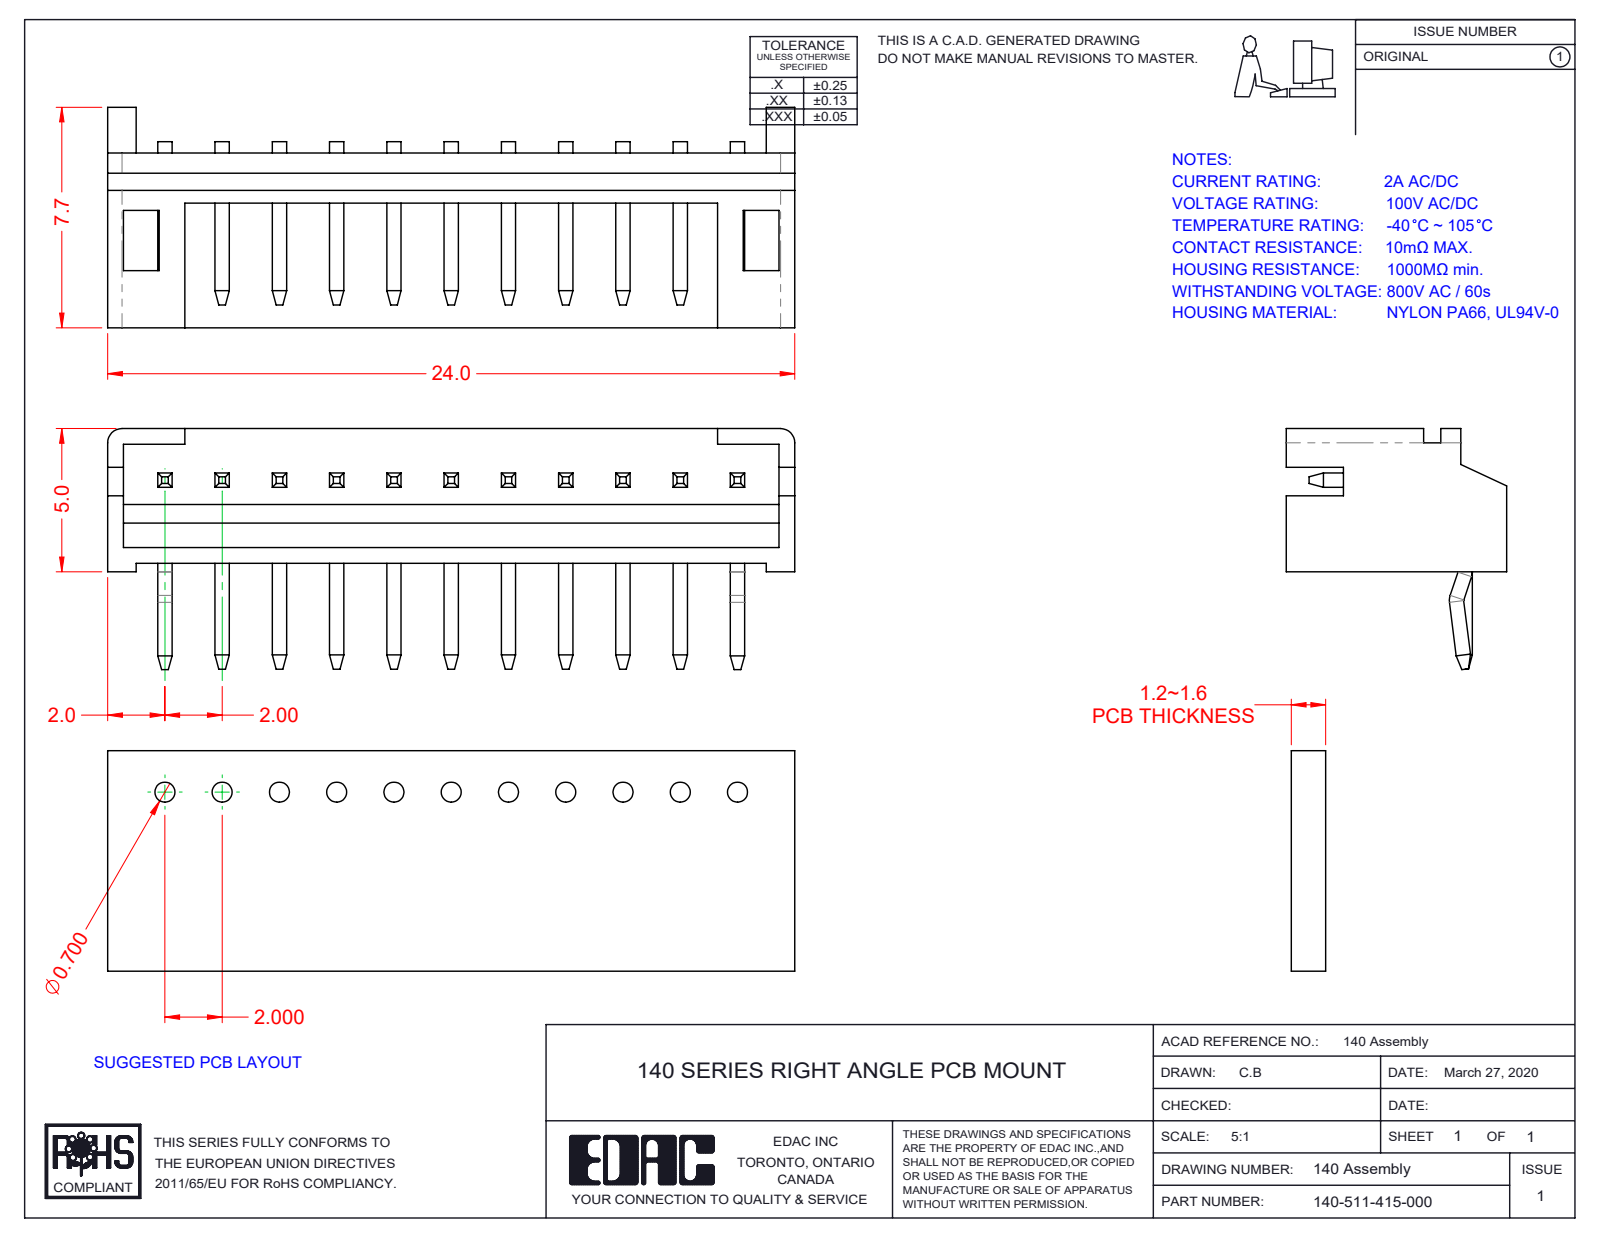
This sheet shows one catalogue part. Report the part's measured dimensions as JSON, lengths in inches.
{"part_name": "140-511-415-000; RA Contact_Kink; RA Housing_511; RA Contact_Str", "step_written_by": "SolidWorks 2016 (CONFIG_CONTROL_DESIGN)", "units": "inches", "bodies": {"solids": 12, "faces": 409, "planar": 375, "cylindrical": 34, "other": 0}, "overall_size": [0.945, 0.331, 0.303], "volume_in3": 0.017, "surface_area_in2": 1.595, "partial_cylinders_radius": [[0.02, 2], [0.022, 2], [0.006, 1], [0.026, 1]], "face_to_face_distances": [0.022, 0.059, 0.02, 0.079, 0.236, 0.157, 0.069, 0.163, 0.039, 0.026]}
